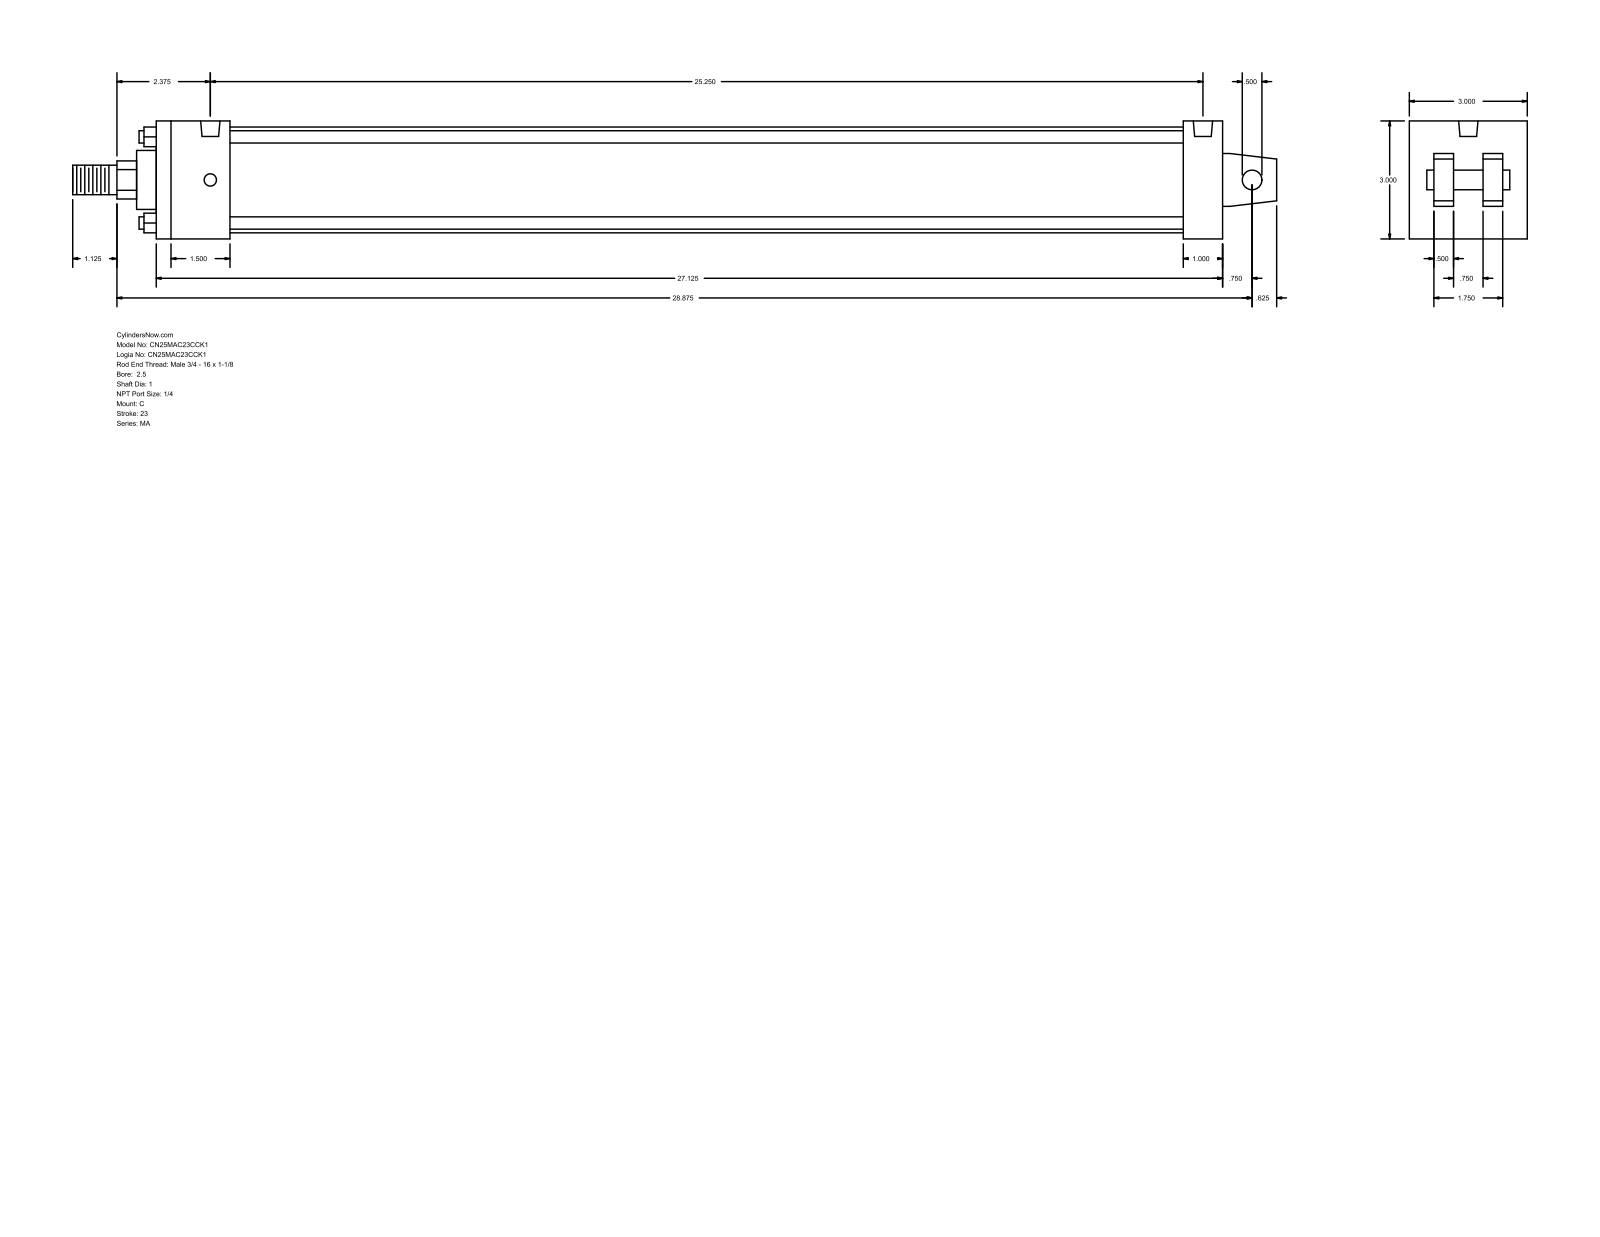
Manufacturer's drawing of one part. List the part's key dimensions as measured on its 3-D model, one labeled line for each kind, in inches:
Part name (STEP PRODUCT): MA_C__0250_1
STEP written by: GSSL Pune (CONFIG_CONTROL_DESIGN)
Units: inches
Bodies: 0 solids, 103 faces (76 planar, 27 cylindrical, 0 other)
Overall size (bounding box): 30.625 × 3 × 3
Round holes (diameter × count): ⌀0.313 ×4, ⌀0.492 ×2
Round bosses / shafts (diameter × count): ⌀0.313 ×4, ⌀2.69 ×1, ⌀1.5 ×1, ⌀1 ×1, ⌀0.75 ×1, ⌀0.5 ×1
Partial cylindrical surfaces — rounded edges, fillets, slot ends (radius × count): R0.484 ×1
Main face-to-face distances: 3, 27.125, 1.875, 0.5, 2.375, 0.625, 1, 1.125, 26.125, 24.25
Hole centre spacings: 25.25
